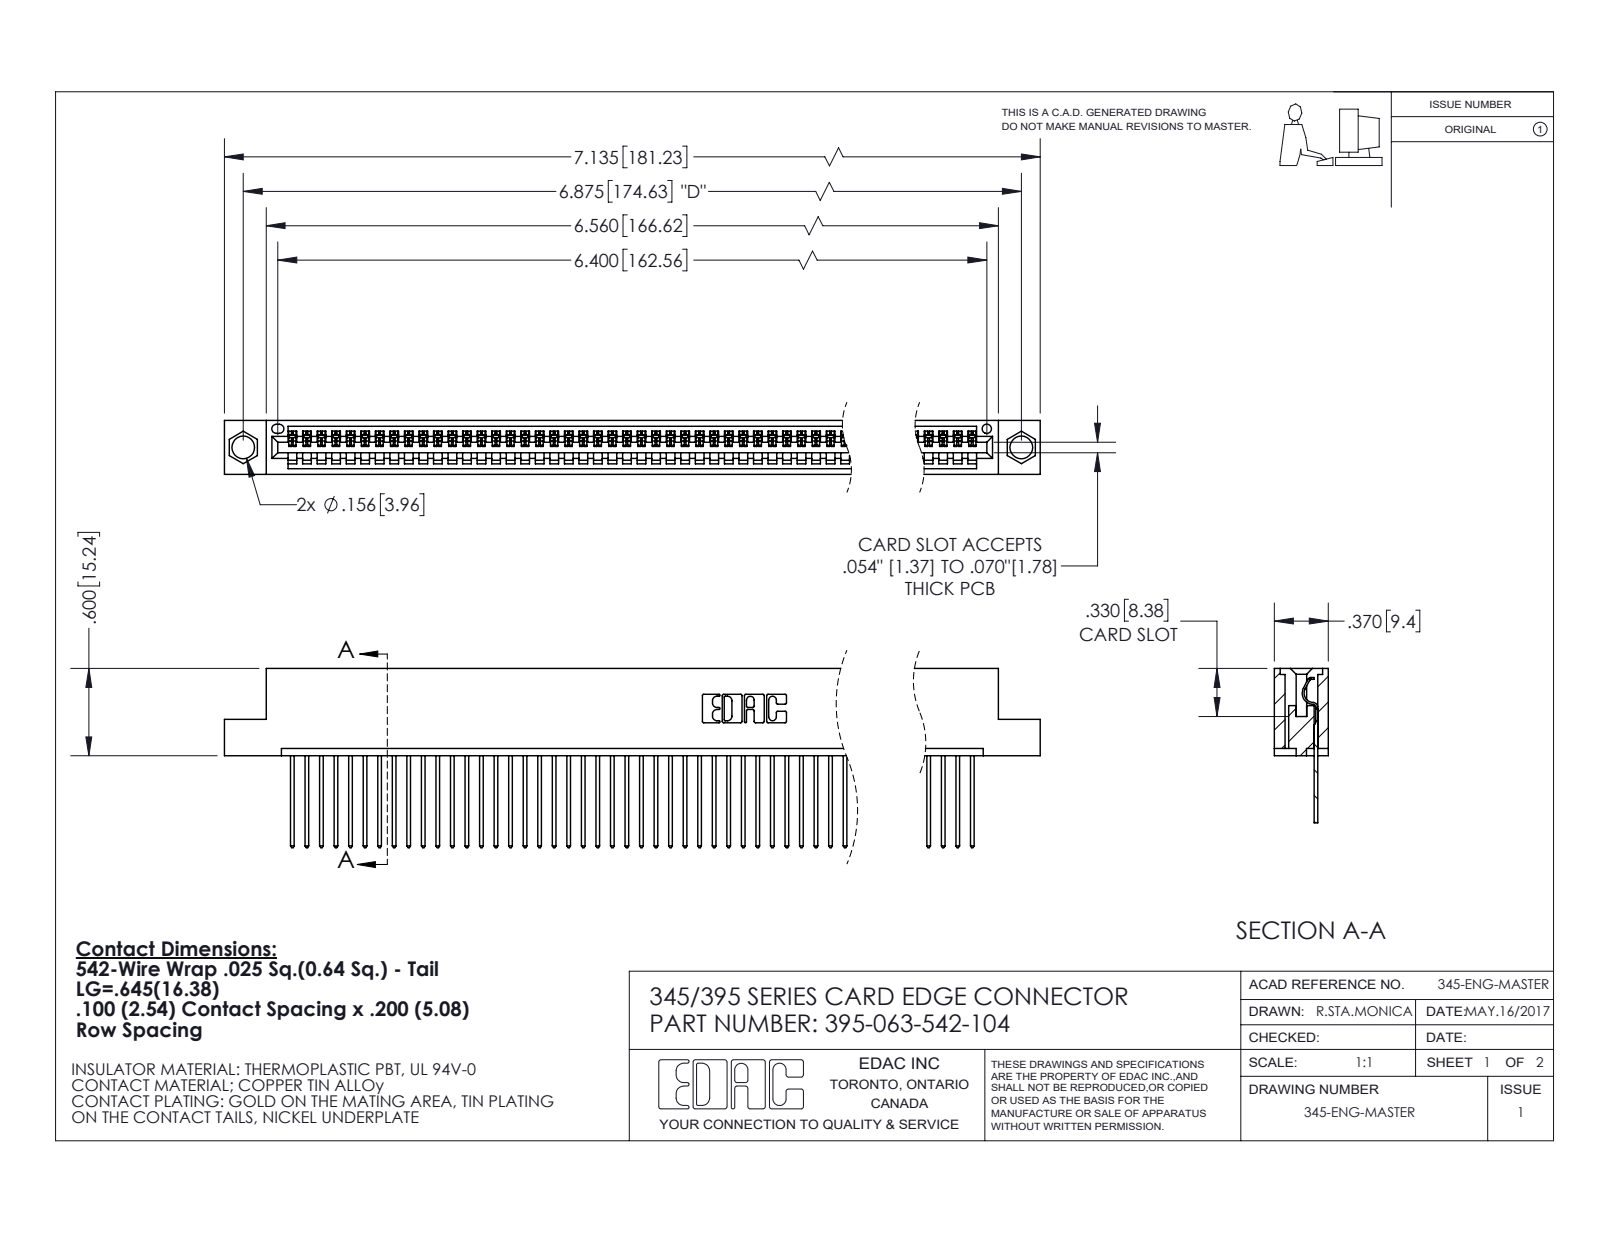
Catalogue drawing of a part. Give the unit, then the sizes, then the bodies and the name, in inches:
Units: inches
Overall size (bounding box): 7.135 × 1.232 × 0.37
Round holes (diameter × count): ⌀0.156 ×2, ⌀0.064 ×1
Partial cylindrical surfaces — rounded edges, fillets, slot ends (radius × count): R0.006 ×126, R0.01 ×126, R0.01 ×22, R0.007 ×6, R0.031 ×6, R0.026 ×3, R0.031 ×2, R0.04 ×2
Main face-to-face distances: 0.072, 0.298, 0.098, 0.272, 0.025, 0.37, 0.2, 0.225, 0.149, 0.072
Hole centre spacings: 0.27, 6.639, 6.875
Volume: 1.063 in³ · Surface area: 37.45 in²
Bodies: 64 solids, 3794 faces (2614 planar, 1180 cylindrical, 0 other)
Part name (STEP PRODUCT): 345-292-001_345-293-142; 395-063-542-104; 345 Part_Flush Mounting Lugs - 0.156 Dia-TI
STEP written by: SolidWorks 2020 (CONFIG_CONTROL_DESIGN)
